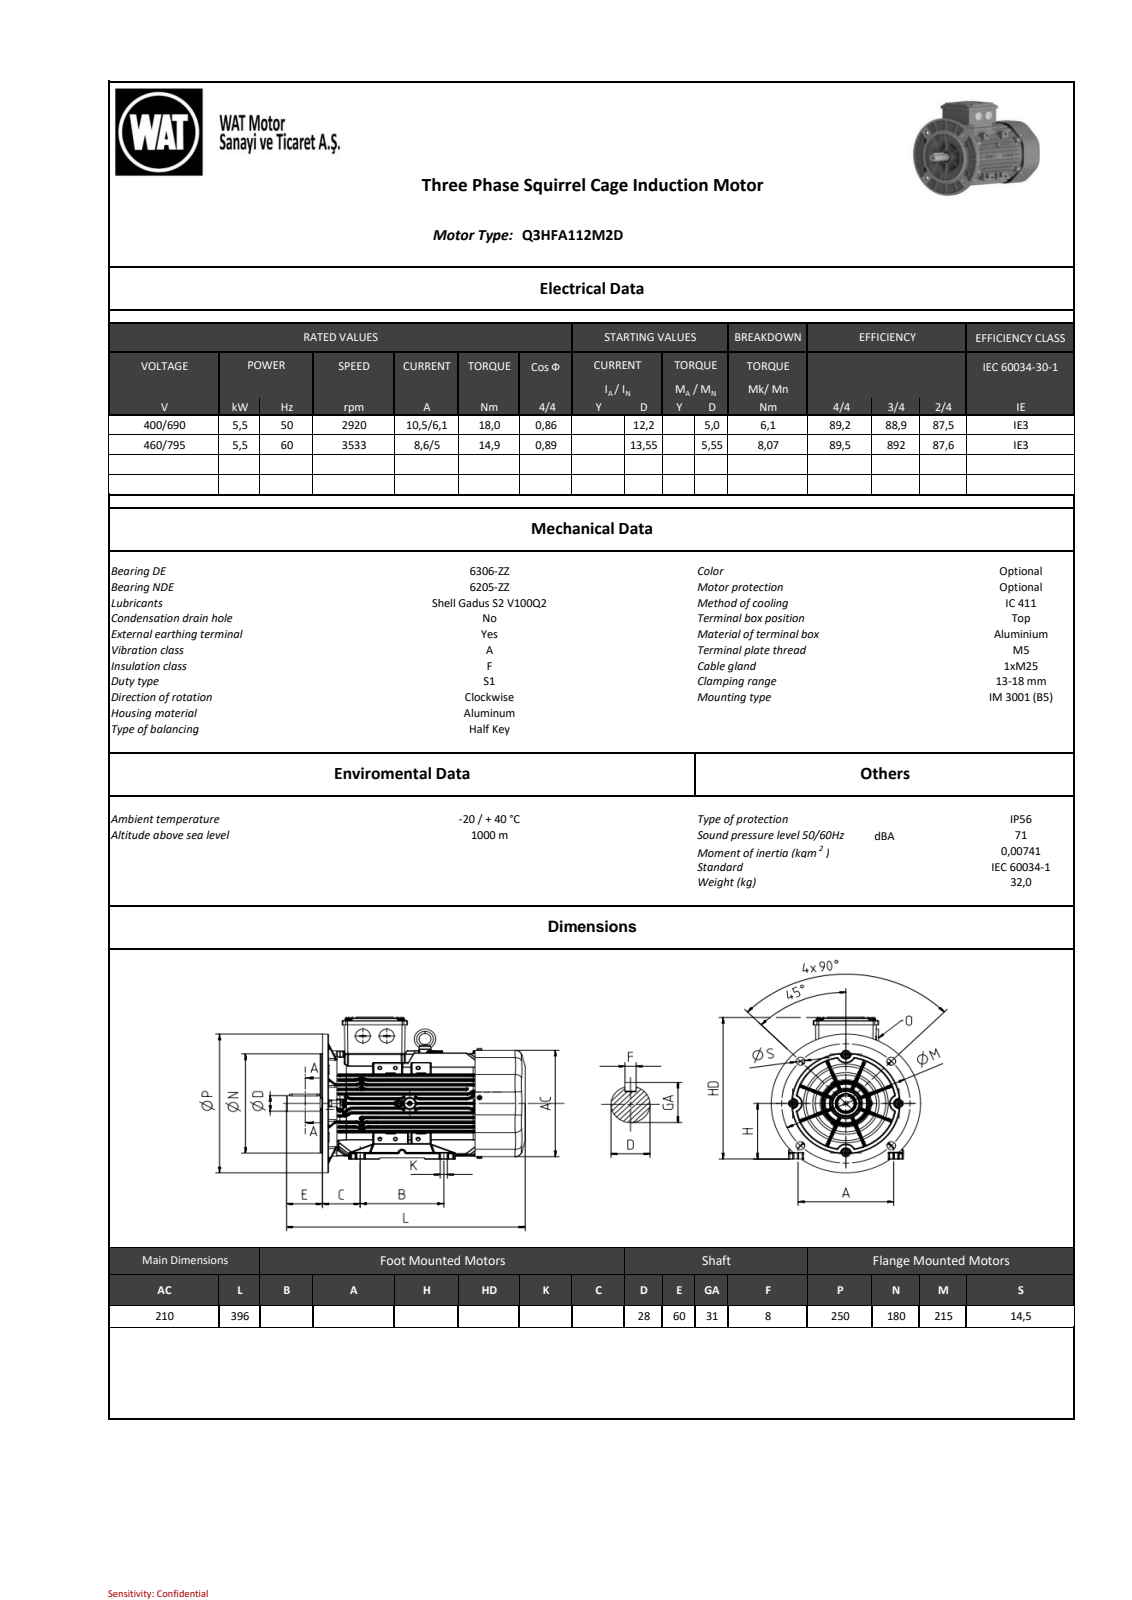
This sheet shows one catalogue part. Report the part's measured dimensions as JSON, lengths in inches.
{"part_name": "QH series_ 112_B5_stp_objects", "step_written_by": "SIEMENS PLM Software NX2206.8101 (AUTOMOTIVE_DESIGN)", "units": "inches", "bodies": {"solids": 0, "faces": 6681, "planar": 1408, "cylindrical": 2480, "other": 2793}, "overall_size": [15.591, 11.314, 9.833], "round_holes": [[0.181, 2], [0.315, 1], [0.335, 1]], "round_bosses_or_shafts": [[0.394, 4], [0.315, 4], [0.984, 2], [0.236, 2], [7.402, 1], [7.087, 1], [1.411, 1], [1.181, 1]], "partial_cylinders_radius": [[0.031, 608], [0.079, 477], [0.02, 315], [0.039, 273], [0.118, 161], [0.157, 10], [0.069, 8], [0.098, 8]], "face_to_face_distances": [0.039, 0.433, 1.416, 0.846, 3.919, 0.983, 3.56, 2.714, 0.363, 1.205]}
